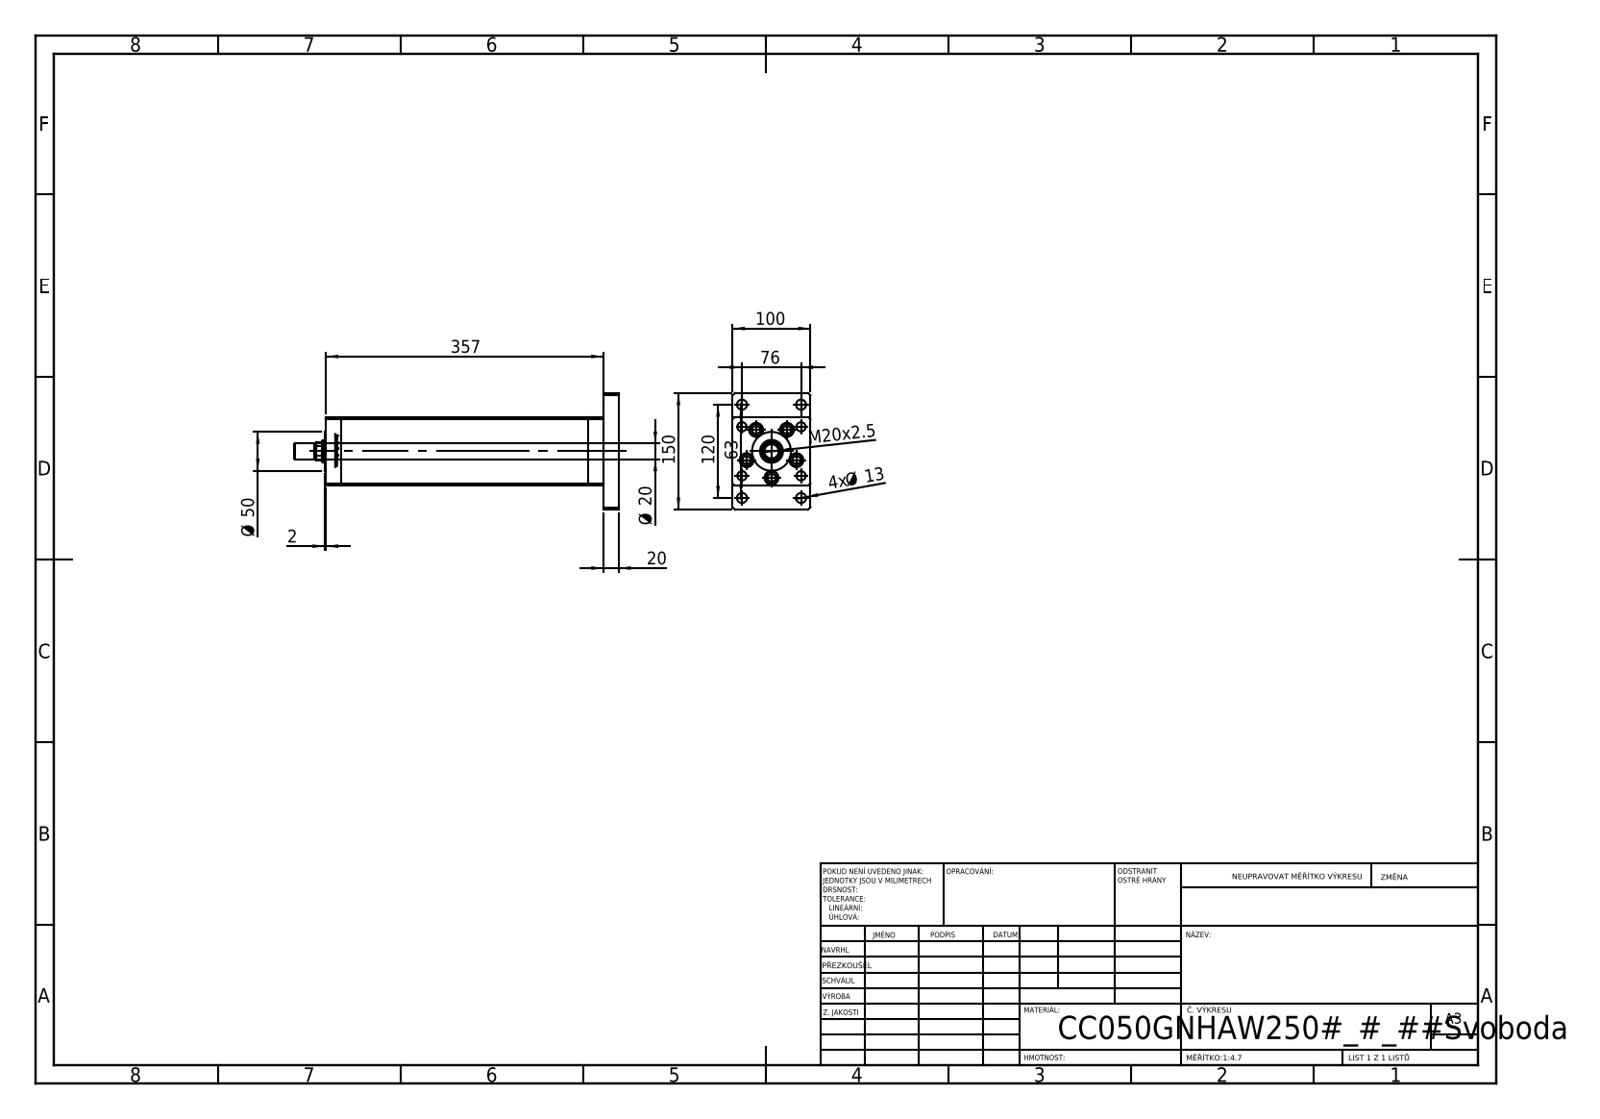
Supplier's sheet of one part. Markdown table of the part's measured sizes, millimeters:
| quantity | value |
| --- | --- |
| part name | V220C_G_MIDDLE; ALLEN BOLT; V220CC_MALE_METRIC; V220C_VC_G (+3 more) |
| STEP written by | SolidWorks 2019 (CONFIG_CONTROL_DESIGN) |
| units | millimeters |
| bodies | 20 solids, 1322 faces (519 planar, 191 cylindrical, 612 other) |
| overall size | 417.5 × 150 × 100 |
| volume | 2 922 000 mm³ |
| surface area | 367 745 mm² |
| round holes (diameter × count) | 12 × 9, 13.5 × 5, 18 × 5, 13 × 4, 17 × 4, 2 × 2, 13.16 × 2, 18.5 × 1, 28 × 1, 29.5 × 1, 68 × 1 |
| round bosses / shafts (diameter × count) | 8 × 9, 17 × 5, 50 × 1, 20 × 1, 18 × 1 |
| partial cylindrical surfaces (radius × count) | 0.93 × 2, 13.5 × 1 |
| main face-to-face distances | 100, 87, 19, 337.5, 318.5, 20, 357.5, 39, 376.5, 356.5 |
| hole center spacings | 34, 28.5, 49.36, 71.02, 76, 81.17, 91.5, 118.95 |
